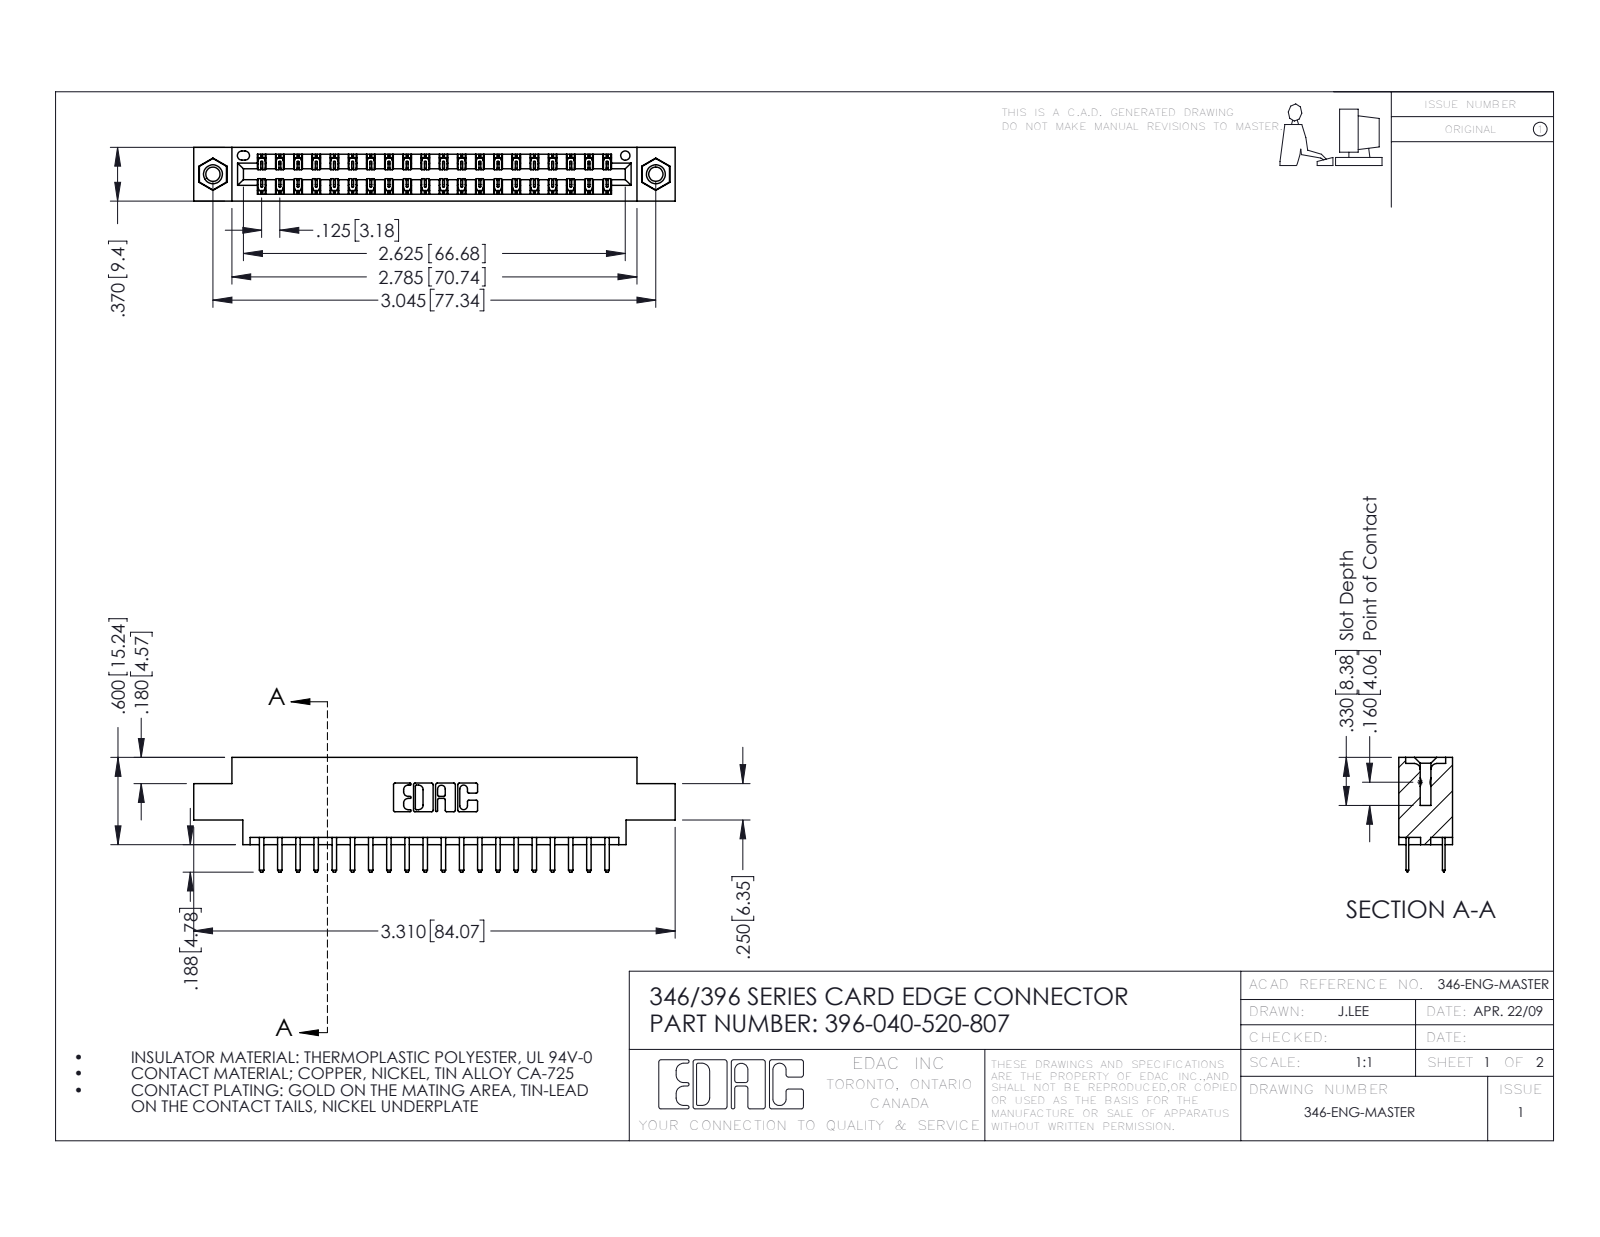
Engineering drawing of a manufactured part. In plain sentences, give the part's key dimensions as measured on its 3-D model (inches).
The part is named "346 Part_0.170 Offset - 0.156 Dia-TI; 396-040-520-807; 345-250-001_345-250-005-103; 345-292-001_345-293-120". Its 3-D file was written by "SolidWorks 2016 (CONFIG_CONTROL_DESIGN)". It is 43 solids with 2426 faces: 1592 planar, 818 cylindrical and 16 other. Overall it measures 3.31 by 0.788 by 0.37 inches. Its volume is 0.479 cubic inches and its surface area 16.44 square inches. Round holes: 2 of diameter 0.098, 2 of diameter 0.125, 2 of diameter 0.156, 1 of diameter 0.064. Round bosses or shafts: 2 of diameter 0.155. Partial cylindrical surfaces (rounded edges, fillets, slot ends): 60 of radius 0.006, 44 of radius 0.01, 22 of radius 0.01, 6 of radius 0.007, 6 of radius 0.031, 3 of radius 0.026, 2 of radius 0.014, 2 of radius 0.022. The main face-to-face distances are 0.048, 0.322, 0.25, 0.37, 0.275, 0.072, 0.298, 0.025, 0.222, 0.148. The hole center spacings are 0.246, 2.837, 3.045.
